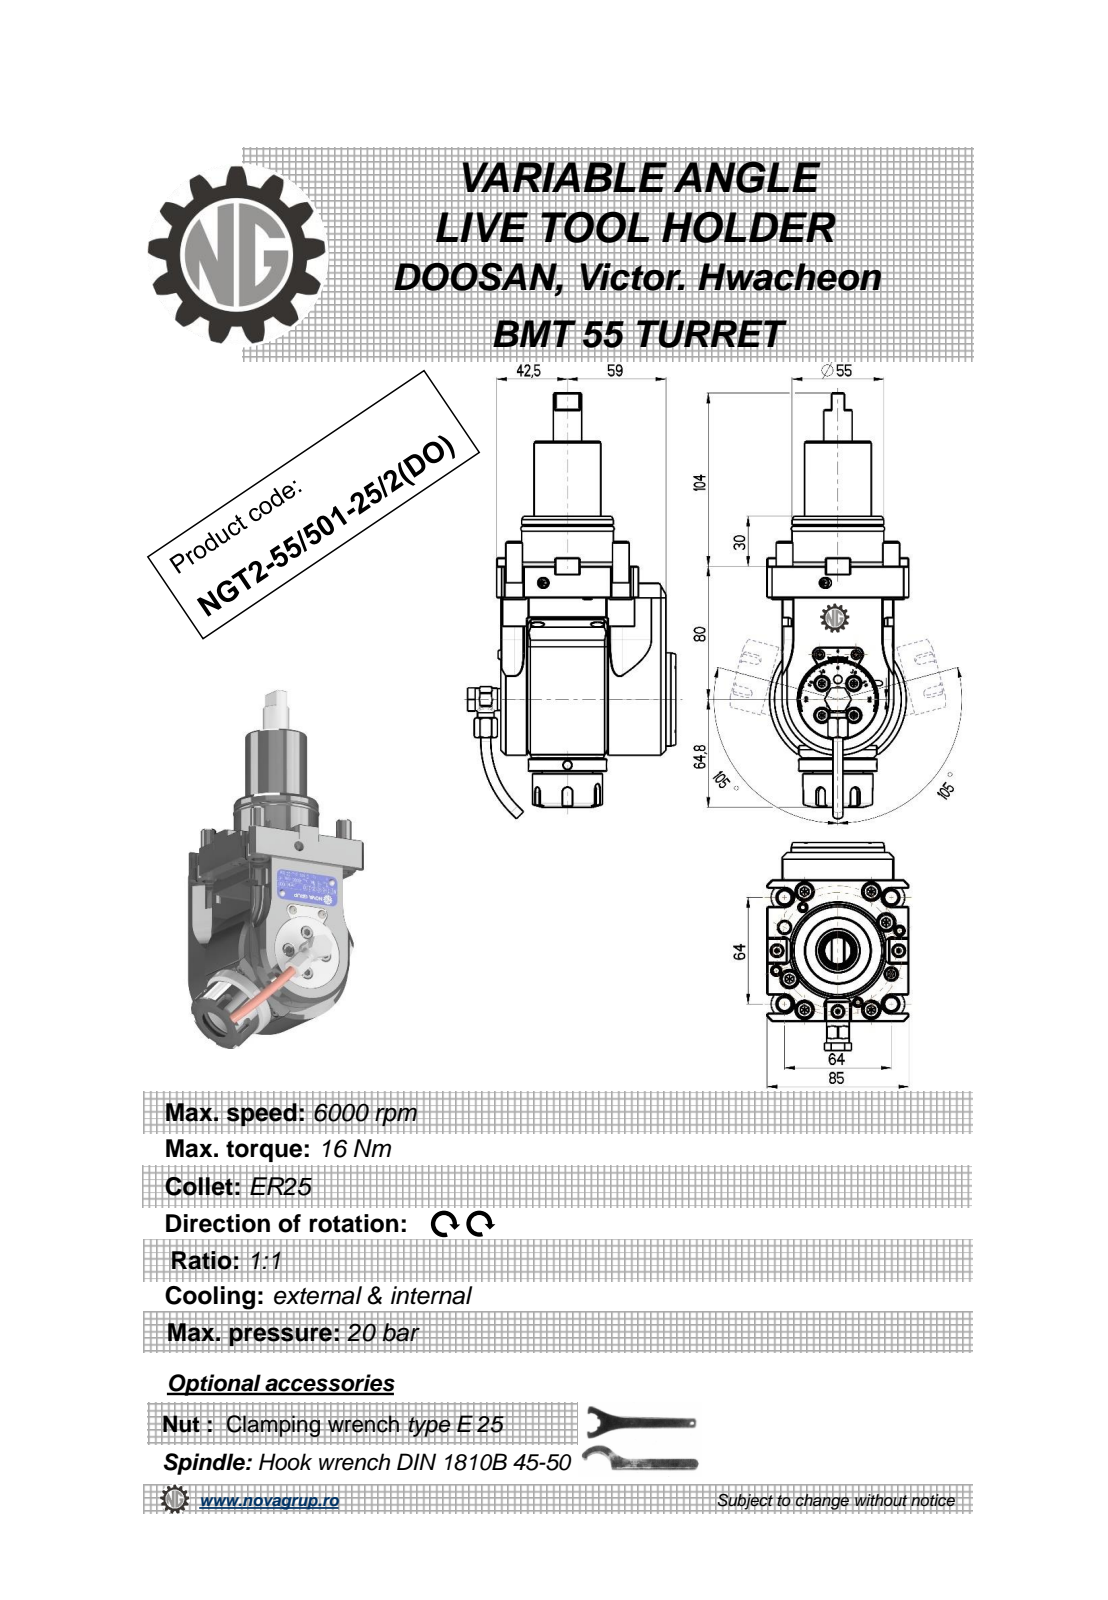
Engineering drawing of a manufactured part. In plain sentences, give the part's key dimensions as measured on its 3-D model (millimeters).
The part is named "NGT2_55_501_25_2_DO". Its 3-D file was written by "PRO/ENGINEER BY PARAMETRIC TECHNOLOGY CORPORATION, 2010280 (CONFIG_CONTROL_DESIGN)". It is 2 solids with 687 faces: 307 planar, 170 cylindrical and 210 other. Overall it measures 255.67 by 124.9 by 85 millimeters. Its volume is 918 954 cubic millimeters and its surface area 93 822 square millimeters. Round holes: 3 of diameter 4, 2 of diameter 5, 2 of diameter 6.8, 1 of diameter 3, 1 of diameter 6.2, 1 of diameter 9, 1 of diameter 11, 1 of diameter 20.3. Round bosses or shafts: 6 of diameter 10, 4 of diameter 6, 2 of diameter 5.7, 1 of diameter 56, 1 of diameter 55, 1 of diameter 54.4, 1 of diameter 50, 1 of diameter 47. Partial cylindrical surfaces (rounded edges, fillets, slot ends): 20 of radius 0.32, 8 of radius 5, 6 of radius 0.41, 5 of radius 3, 4 of radius 0.5, 4 of radius 5.5, 4 of radius 8, 4 of radius 8.5. The main face-to-face distances are 31, 9, 85, 99, 66.5, 6, 16, 2.5, 105, 76. The hole center spacings are 34.93, 0.4, 39.45, 47.42, 47.72, 49, 49.4, 69.86.
